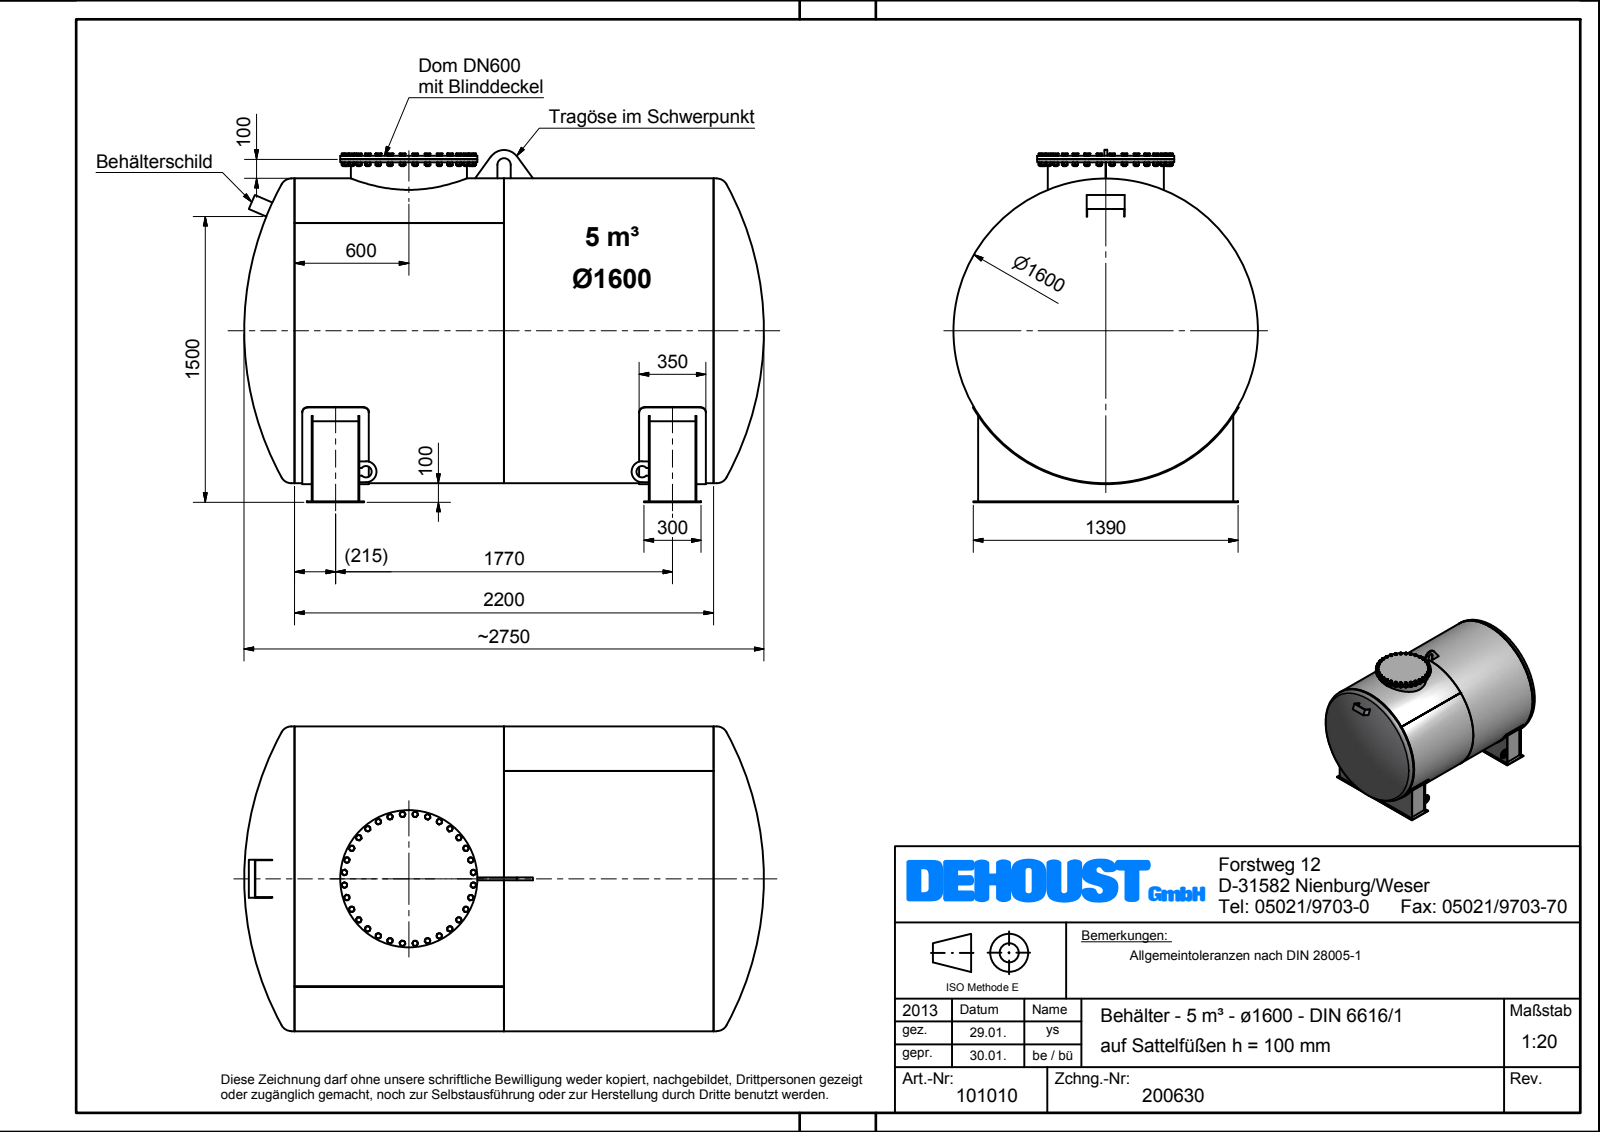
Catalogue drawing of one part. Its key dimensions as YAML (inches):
part_name: "Beh\\S\\dlter_6616_E_1600_005_100_KV"
step_written_by: "Autodesk Inventor 2012 (AUTOMOTIVE_DESIGN)"
units: inches
bodies: {solids: 3, faces: 1109, planar: 656, cylindrical: 161, other: 292}
overall_size: [107.5, 72.835, 62.992]
volume: 44800
surface_area: 57510
round_holes:
  - {diameter: 23.543, count: 1}
  - {diameter: 62.598, count: 1}
round_bosses_or_shafts:
  - {diameter: 0.976, count: 32}
  - {diameter: 0.709, count: 32}
  - {diameter: 0.656, count: 32}
  - {diameter: 62.992, count: 1}
  - {diameter: 28.346, count: 1}
  - {diameter: 25.984, count: 1}
  - {diameter: 24.016, count: 1}
partial_cylinders:
  - {radius: 1.181, count: 8}
  - {radius: 1.17, count: 2}
  - {radius: 2.165, count: 2}
  - {radius: 1.378, count: 1}
  - {radius: 3.346, count: 1}
  - {radius: 31.693, count: 1}
face_to_face_distances: [0.197, 86.614, 69.685, 9.646, 3.543, 83.071, 13.386, 73.228, 9.843, 3.74]
